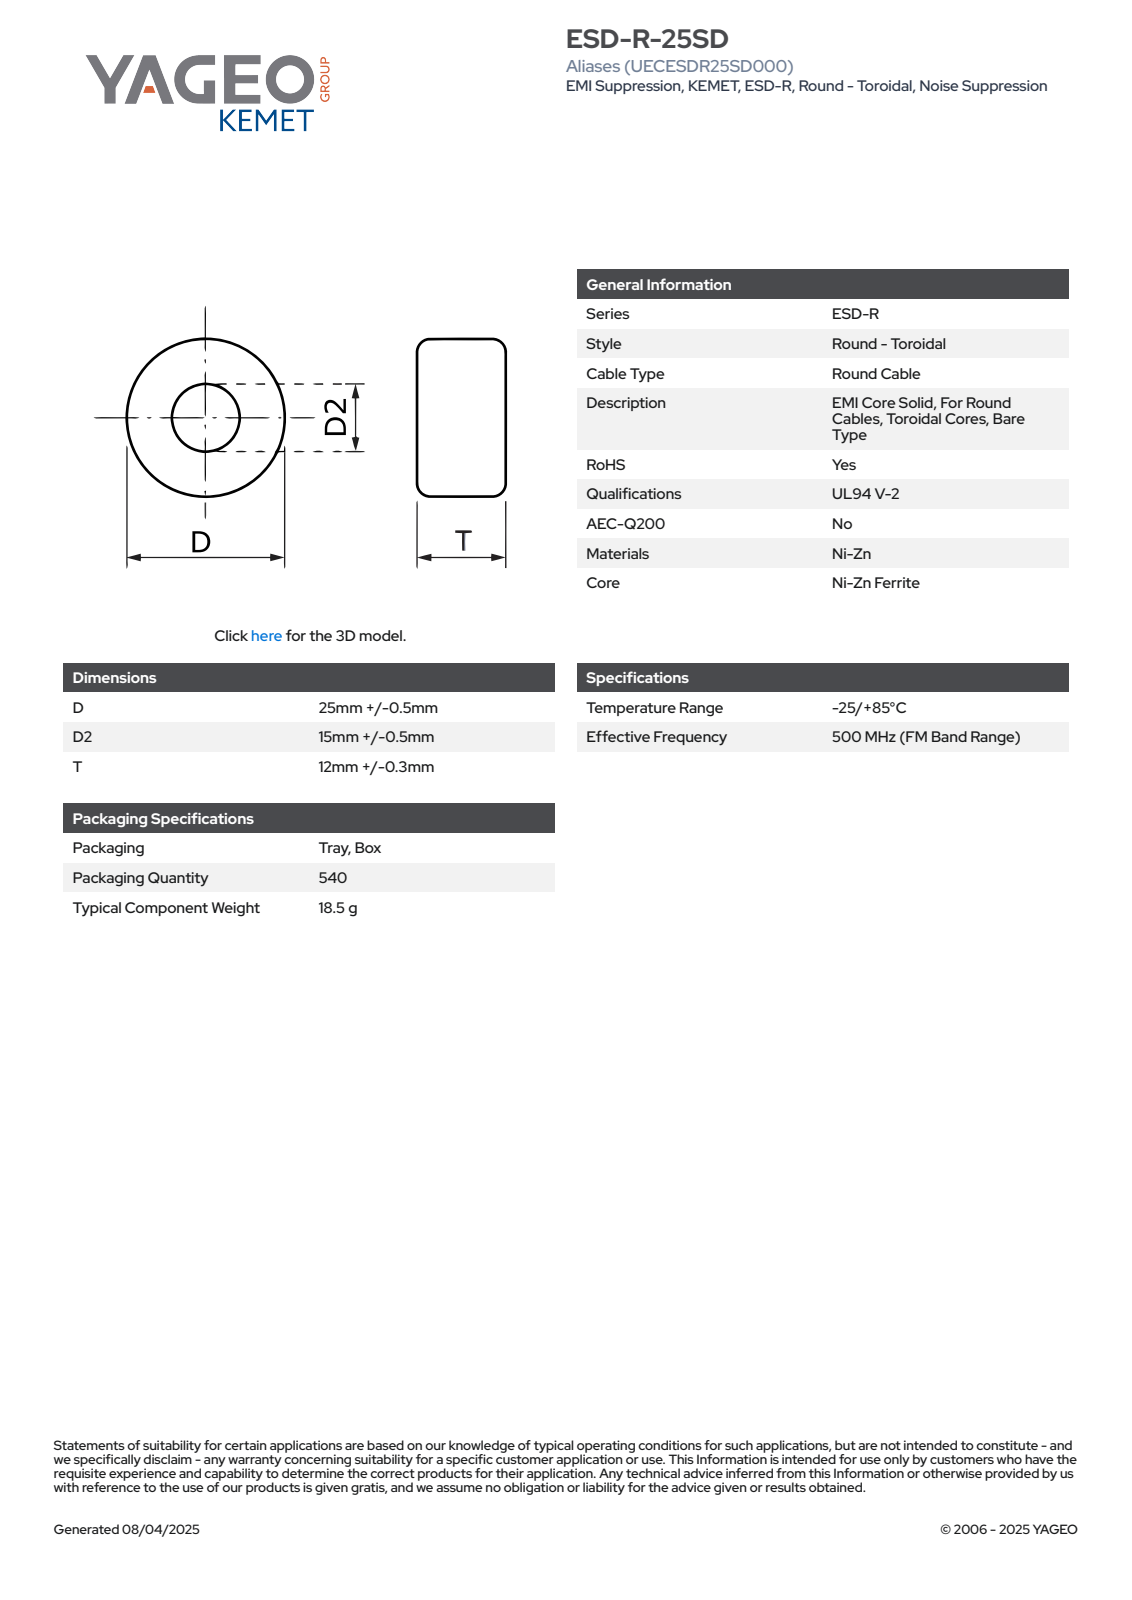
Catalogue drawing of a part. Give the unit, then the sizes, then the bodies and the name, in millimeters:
Units: millimetres
Overall size (bounding box): 25.51 × 25.5 × 12.3
Round holes (diameter × count): ⌀15 ×1
Round bosses / shafts (diameter × count): ⌀25.5 ×1
Partial cylindrical surfaces — rounded edges, fillets, slot ends (radius × count): R12.76 ×1
Main face-to-face distances: 12.3, 5.3, 7, 1.7, 0.32, 5.62, 6.68, 1.38, 1.06, 6.36
Volume: 4 086 mm³ · Surface area: 2 183 mm²
Bodies: 1 solid, 66 faces (24 planar, 7 cylindrical, 35 other)
Part name (STEP PRODUCT): EC_KBC_D25.5D215T12.3
STEP written by: SolidWorks 2021 (AUTOMOTIVE_DESIGN)
